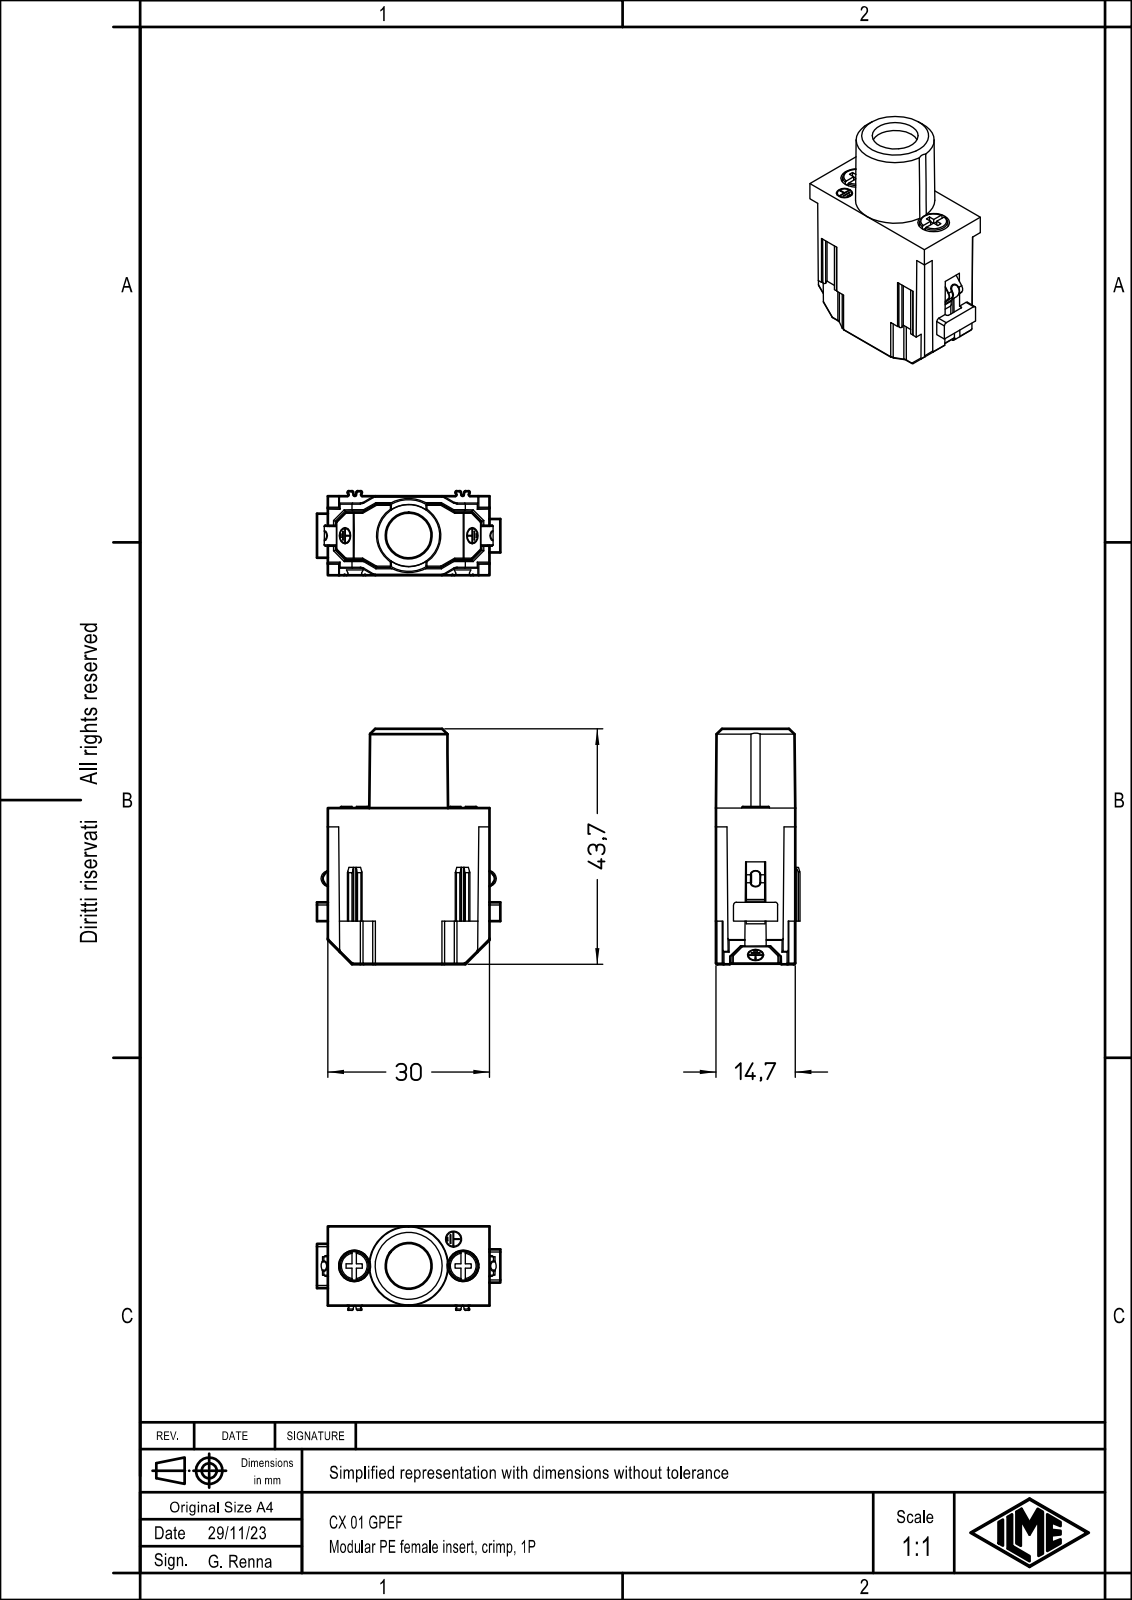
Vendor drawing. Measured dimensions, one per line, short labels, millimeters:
name: CX 01 GPEF
written by: Creo Elements/Direct Modeling 20.1B 02-Apr-2019 (C) Parametric Technology GmbH (AUTOMOTIVE_DESIGN)
unit: mm
bodies: 1 solid, 446 faces (210 planar, 168 cylindrical, 68 other)
size: 43.7 × 34 × 15.6
volume: 8 695 mm³; area: 7 361 mm²
holes: 1× ⌀8.5, 1× ⌀11.5, 1× ⌀13.3
bosses: 2× ⌀5.5
rounds: 104× R0.2, 12× R0.5, 10× R1, 2× R1.15, 1× R6.7, 1× R8.15
face distances: 14.7, 2, 30, 1, 7.3, 5.3, 22.7, 7.9, 2.05, 12.65
